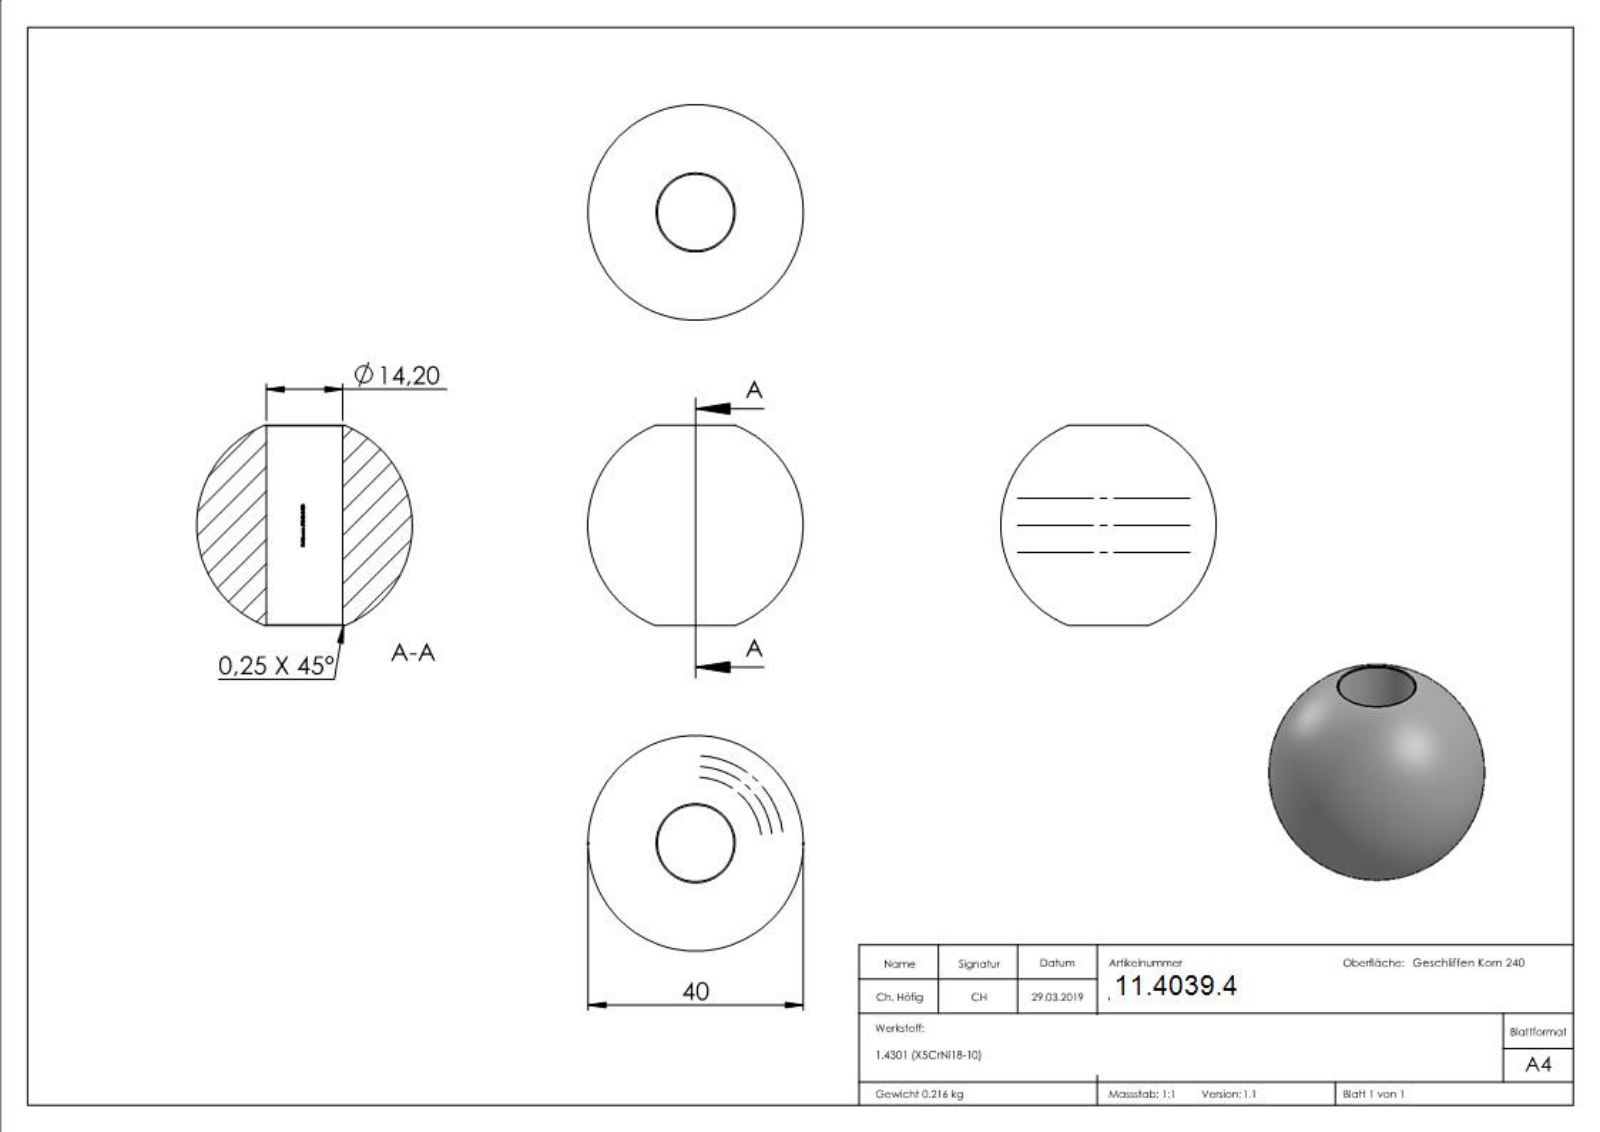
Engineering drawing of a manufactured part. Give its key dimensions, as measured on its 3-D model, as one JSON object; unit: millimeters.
{"part_name": "51040-240D", "step_written_by": "SolidWorks 2015 (CONFIG_CONTROL_DESIGN)", "units": "millimeters", "bodies": {"solids": 1, "faces": 239, "planar": 108, "cylindrical": 29, "other": 102}, "overall_size": [40, 40, 37.22], "volume_mm3": 27377, "surface_area_mm2": 6352, "round_holes": [[14.2, 1]], "partial_cylinders_radius": [[7.2, 1]], "face_to_face_distances": [2.98, 1.47, 1.19, 5.19, 5.85, 0.35, 0.66, 1.74, 0.61, 0.55]}
